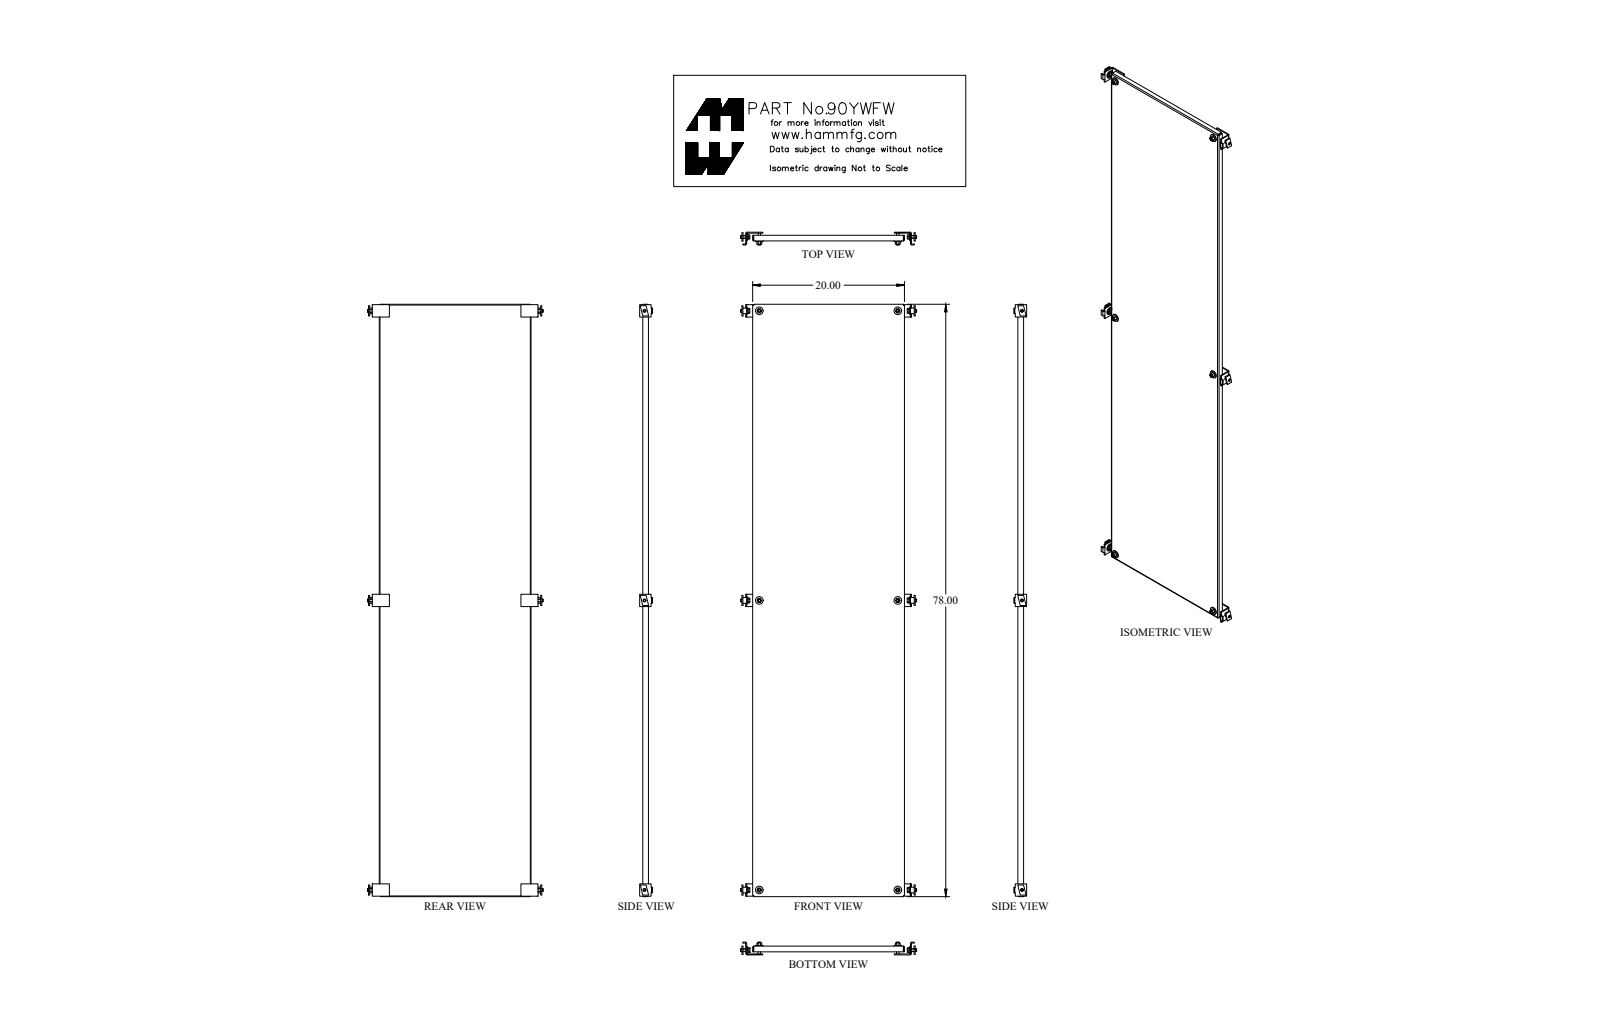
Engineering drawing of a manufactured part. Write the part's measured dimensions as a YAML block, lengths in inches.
part_name: "90YWFW_Default"
step_written_by: "SolidWorks 2018 (CONFIG_CONTROL_DESIGN)"
units: inches
bodies: {solids: 1, faces: 42, planar: 22, cylindrical: 20, other: 0}
overall_size: [78, 20, 0.75]
volume: 159.4
surface_area: 3376
round_holes:
  - {diameter: 0.563, count: 6}
partial_cylinders:
  - {radius: 0.048, count: 4}
  - {radius: 0.143, count: 4}
face_to_face_distances: [0.095, 19.905, 19.81, 20, 77.905, 0.75, 0.655, 78, 77.81, 0.143]
hole_center_spacings: [38.125, 42.268, 18.25, 76.25, 78.404]
